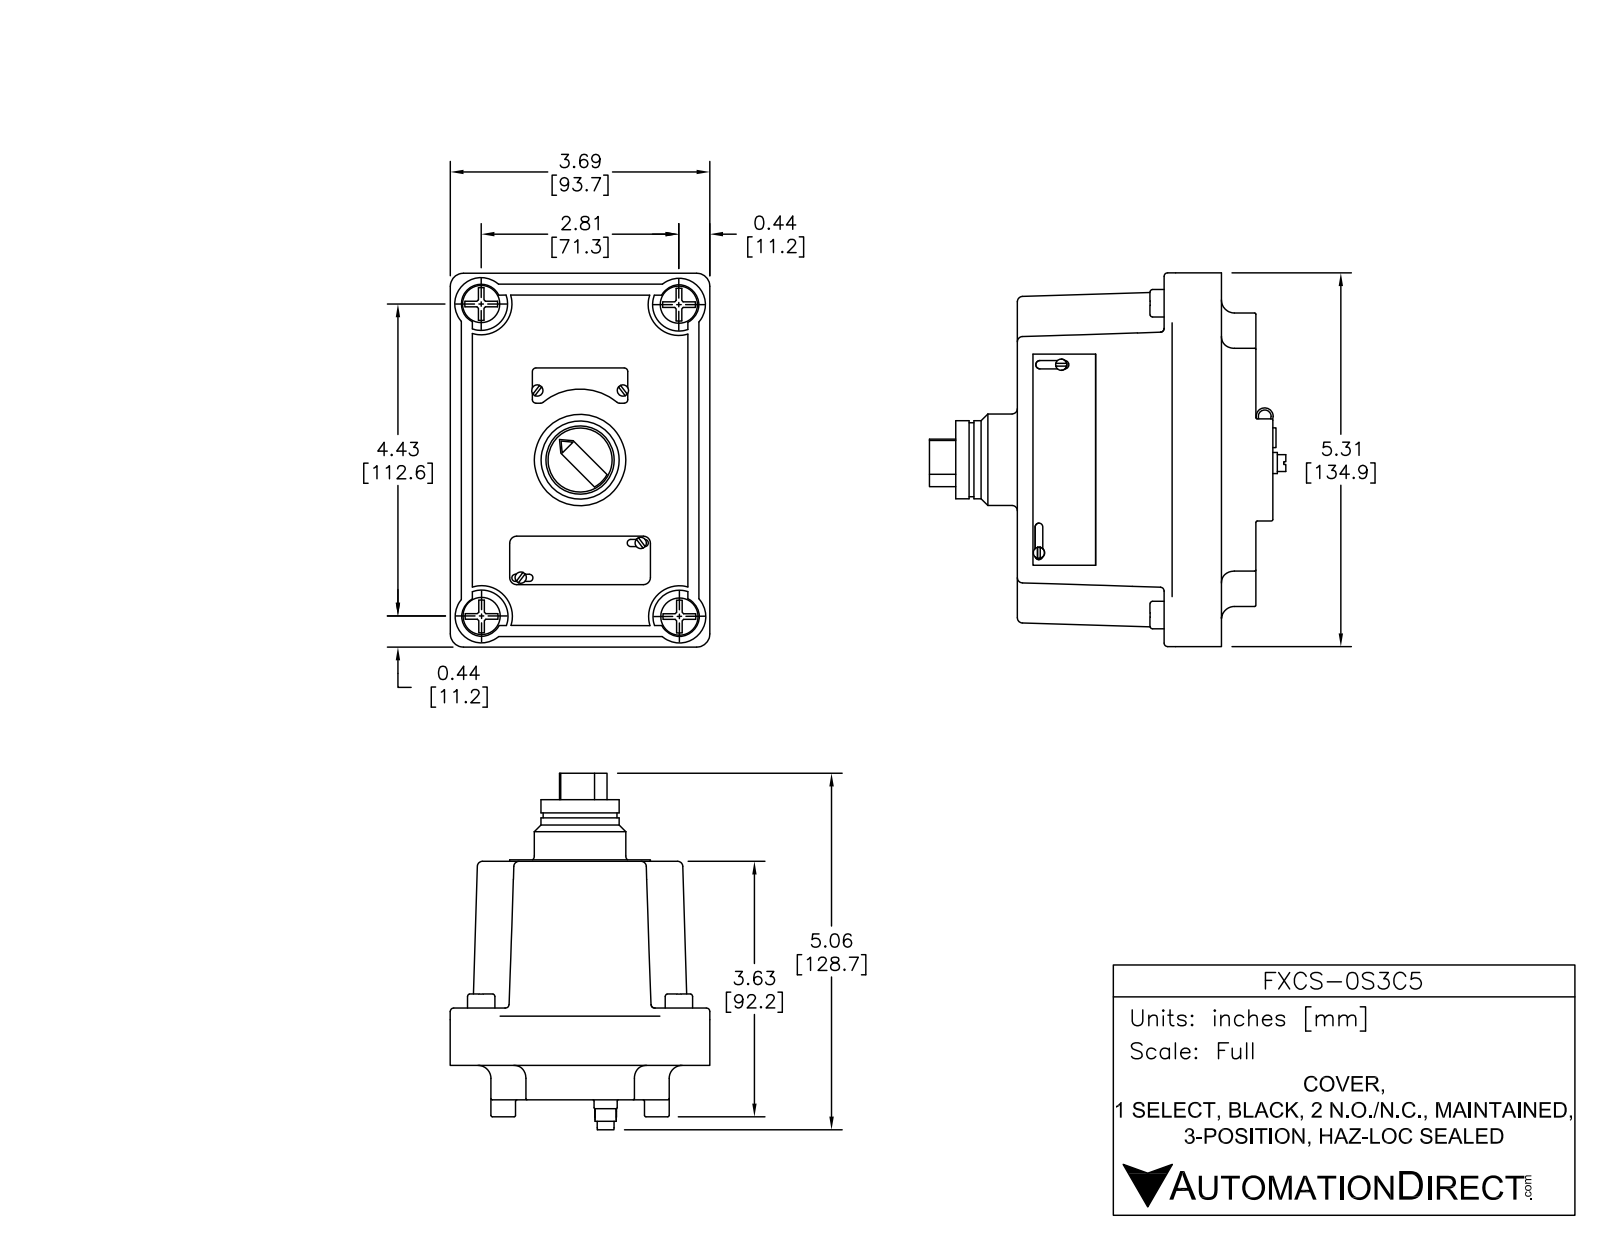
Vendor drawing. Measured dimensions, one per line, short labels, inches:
name: FXCS-0S3C5
written by: SolidWorks 2015 (AUTOMOTIVE_DESIGN)
unit: in
bodies: 2 solids, 710 faces (308 planar, 166 cylindrical, 236 other)
size: 5.31 × 5.066 × 3.69
volume: 48.91 in³; area: 100.9 in²
holes: 8× ⌀0.16, 1× ⌀0.198, 1× ⌀0.97
bosses: 8× ⌀0.16, 4× ⌀0.39, 1× ⌀1.3, 1× ⌀1.11, 1× ⌀1.05, 1× ⌀0.91, 1× ⌀0.33, 1× ⌀0.3
rounds: 24× R0.05, 22× R0.02, 4× R0.051, 4× R0.055, 4× R0.06, 4× R0.075, 4× R0.1, 4× R0.185
face distances: 3.39, 0.49, 2.9, 0.021, 3.69, 0.578, 3.111, 1.19, 0.7, 2.2
hole spacings: 0.25, 2.197, 0.5, 2.183, 2.239, 0.75, 1.092, 1.115
